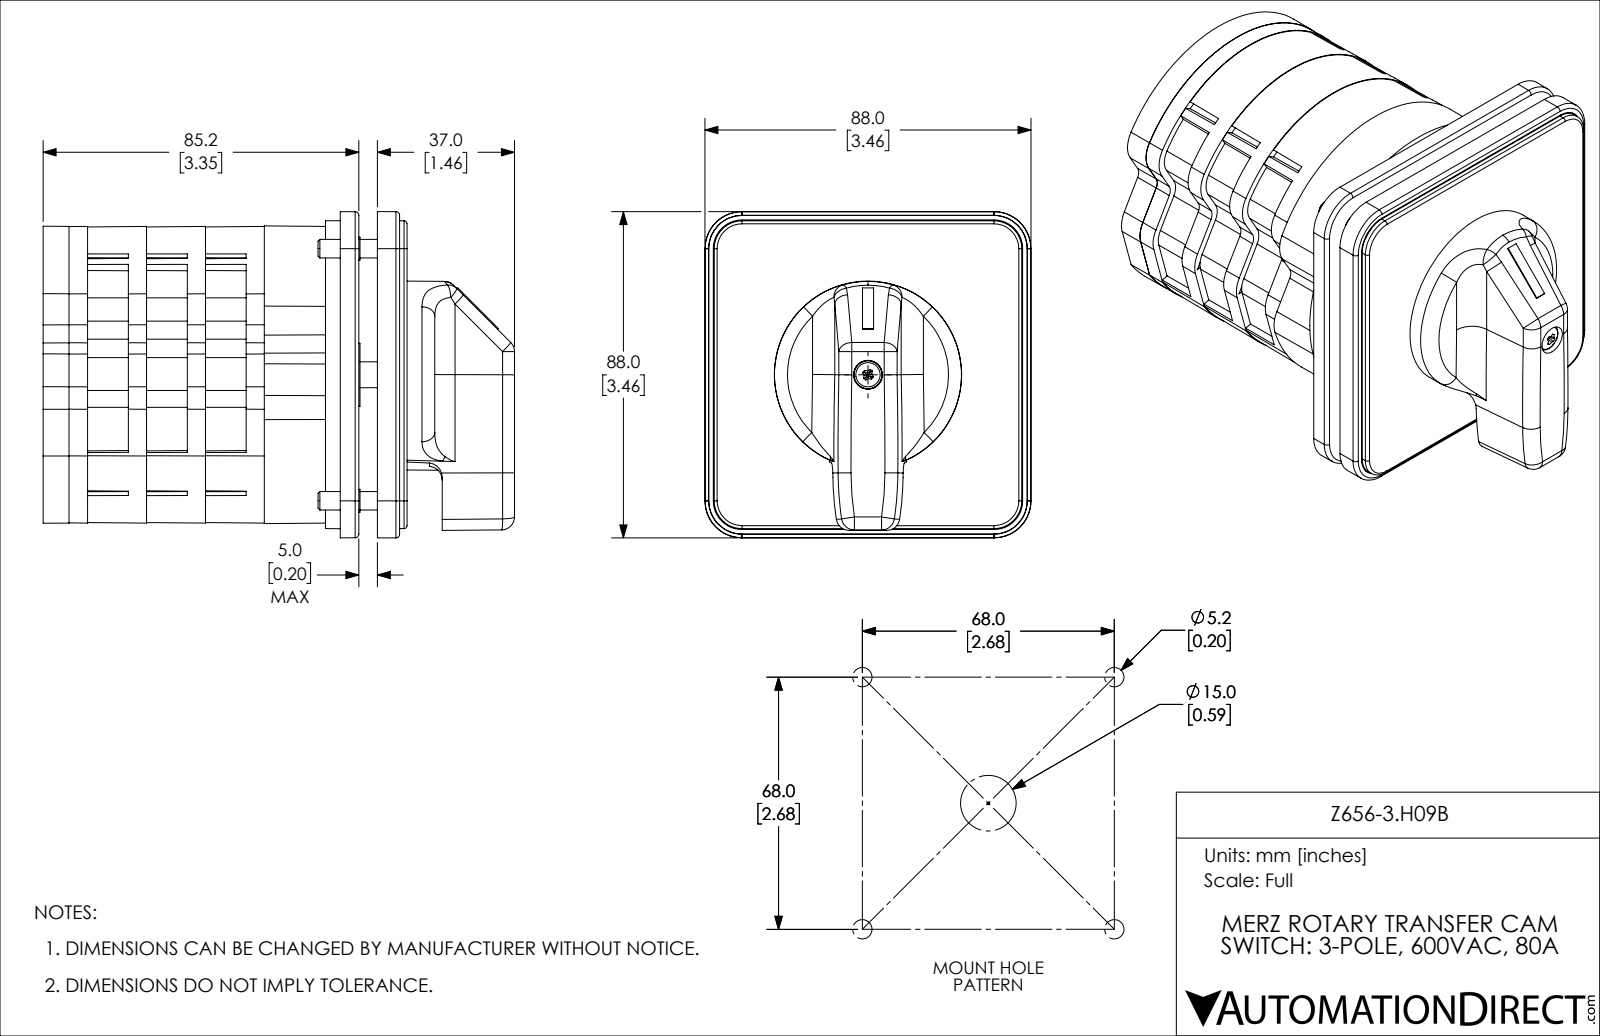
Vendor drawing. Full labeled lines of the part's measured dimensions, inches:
Part name (STEP PRODUCT): Z656-3.H09B
STEP written by: SolidWorks 2021 (CONFIG_CONTROL_DESIGN)
Units: inches
Bodies: 16 solids, 2724 faces (1518 planar, 430 cylindrical, 776 other)
Overall size (bounding box): 5.008 × 3.465 × 3.465
Volume: 24.66 in³ · Surface area: 232.4 in²
Round holes (diameter × count): ⌀0.315 ×13, ⌀0.201 ×10, ⌀0.205 ×8, ⌀0.374 ×8, ⌀0.177 ×6, ⌀0.165 ×4, ⌀0.169 ×4, ⌀0.236 ×4, ⌀0.339 ×4, ⌀0.197 ×2, ⌀0.228 ×2, ⌀0.256 ×2
Round bosses / shafts (diameter × count): ⌀0.319 ×7, ⌀0.295 ×5, ⌀0.197 ×5, ⌀0.157 ×5, ⌀0.366 ×4, ⌀0.287 ×4, ⌀0.244 ×4, ⌀1.181 ×1
Partial cylindrical surfaces — rounded edges, fillets, slot ends (radius × count): R0.039 ×18, R0.008 ×14, R0.02 ×12, R0.236 ×8, R0.138 ×6, R0.031 ×4, R0.256 ×4, R0.295 ×4
Main face-to-face distances: 0.079, 0.354, 0.626, 0.059, 0.157, 0.709, 0.866, 0.65, 0.433, 0.787
Hole centre spacings: 0.904, 0.895, 0.974, 1.48, 1.824, 1.831, 1.904, 2.27
